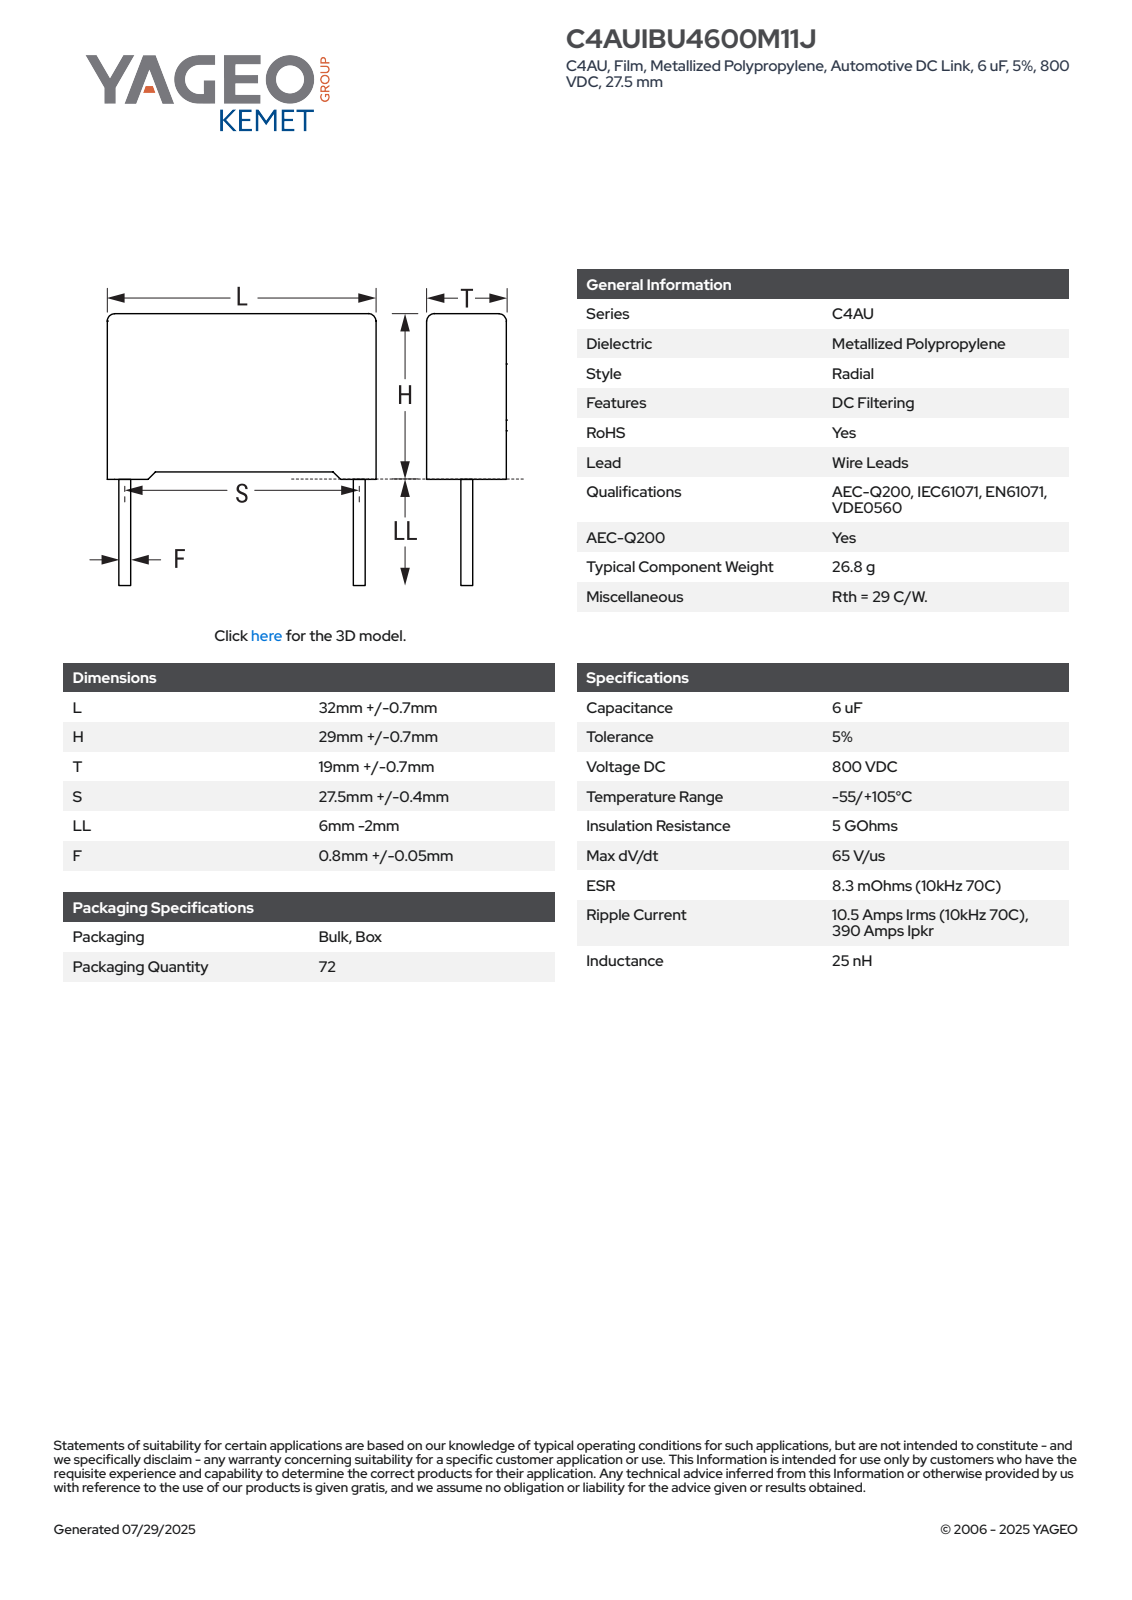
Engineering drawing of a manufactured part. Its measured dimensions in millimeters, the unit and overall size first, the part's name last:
Units: millimetres
Overall size (bounding box): 33.7 × 32.7 × 19.7
Round bosses / shafts (diameter × count): ⌀0.85 ×2
Partial cylindrical surfaces — rounded edges, fillets, slot ends (radius × count): R0.5 ×4
Main face-to-face distances: 19.7, 32.7, 28.68, 28.95, 0.75, 1.02, 29.7, 1.09, 31.61, 19.71
Volume: 18 569 mm³ · Surface area: 4 478 mm²
Bodies: 4 solids, 85 faces (77 planar, 8 cylindrical, 0 other)
Part name (STEP PRODUCT): CFR_RB2CFP_32X29X19_L32.7H29.7T19.7S27.5LL4F0.85
STEP written by: SolidWorks 2014 (AUTOMOTIVE_DESIGN)
